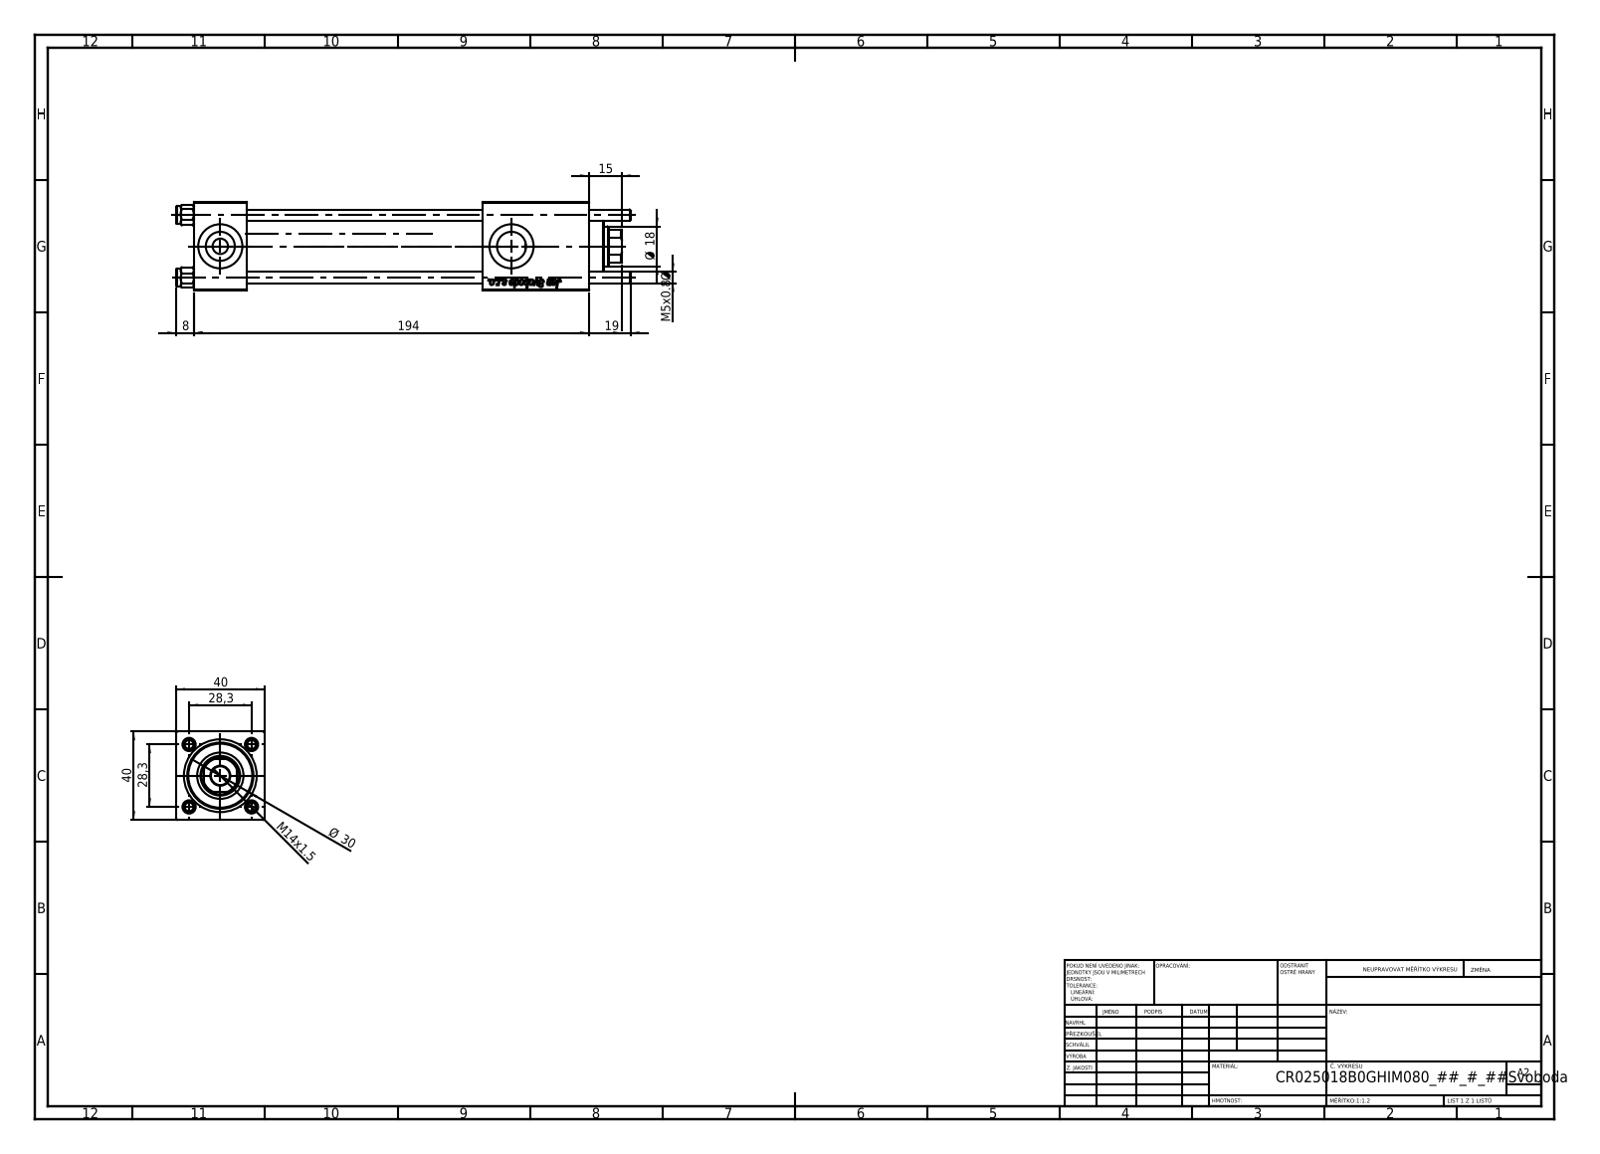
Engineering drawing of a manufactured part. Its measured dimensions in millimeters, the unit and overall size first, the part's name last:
Units: millimetres
Overall size (bounding box): 206 × 40 × 40
Round holes (diameter × count): ⌀5 ×4, ⌀20 ×3, ⌀7 ×2, ⌀13.16 ×2, ⌀8.5 ×1, ⌀18 ×1, ⌀21 ×1, ⌀25 ×1, ⌀30 ×1
Round bosses / shafts (diameter × count): ⌀8 ×4, ⌀31 ×1
Partial cylindrical surfaces — rounded edges, fillets, slot ends (radius × count): R8.5 ×1
Main face-to-face distances: 40, 24, 131, 107, 150.3, 126.3, 19.3, 179, 155, 48
Hole centre spacings: 20.01, 28.3, 40.02, 132
Volume: 188 305 mm³ · Surface area: 78 613 mm²
Bodies: 11 solids, 1152 faces (428 planar, 76 cylindrical, 648 other)
Part name (STEP PRODUCT): NUT_M5_B; V215_VC_A; V215CR_B_TYCINKA; V215CR_B-1 (+1 more)
STEP written by: SolidWorks 2019 (CONFIG_CONTROL_DESIGN)
